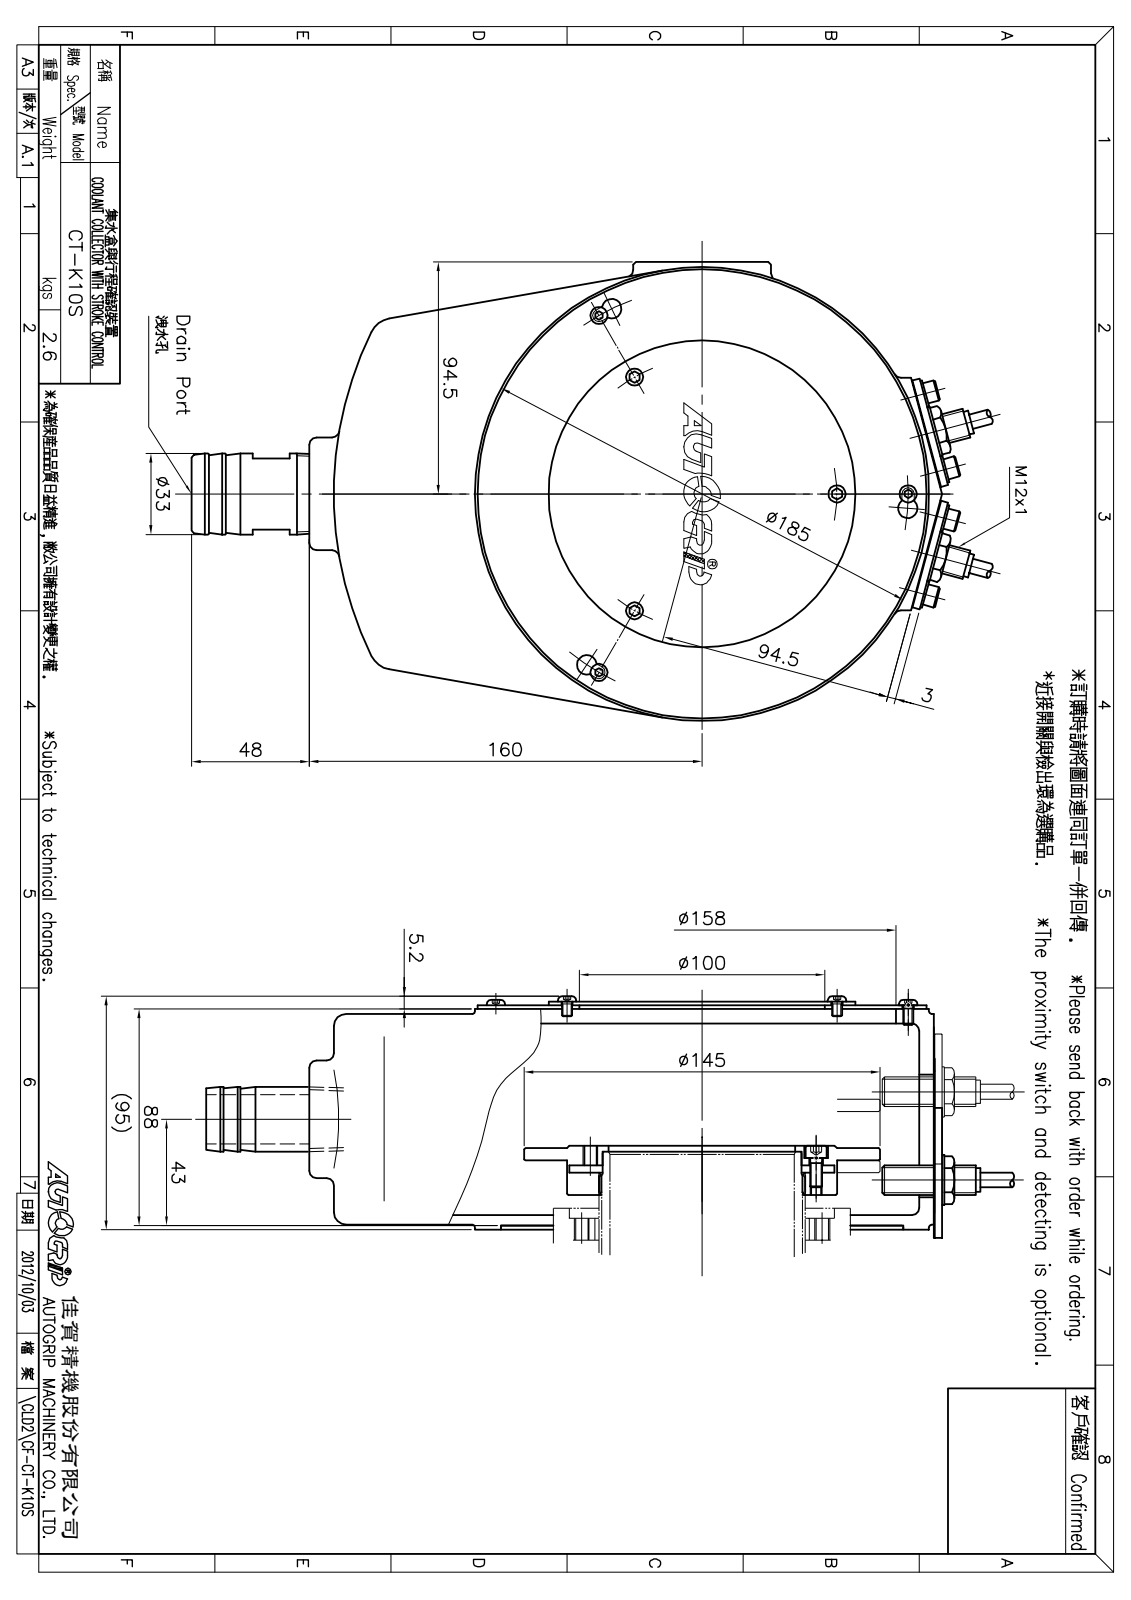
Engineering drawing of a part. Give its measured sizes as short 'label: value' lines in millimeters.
name: CF-CT-10集水盒本體; CF-CT-08洩油管; CF-CT-K10S; N5x12_M5x14 (+2 more)
written by: SolidWorks 2016 (CONFIG_CONTROL_DESIGN)
unit: mm
bodies: 25 solids, 680 faces (314 planar, 220 cylindrical, 146 other)
size: 312.28 × 187 × 95
volume: 630 546 mm³; area: 343 614 mm²
holes: 6× ⌀4, 6× ⌀5, 6× ⌀5.5, 3× ⌀4.5, 2× ⌀6, 2× ⌀9.5, 2× ⌀12, 1× ⌀25, 1× ⌀76, 1× ⌀81, 1× ⌀84, 1× ⌀100
bosses: 6× ⌀8.5, 6× ⌀7, 4× ⌀11, 2× ⌀5, 1× ⌀185, 1× ⌀183, 1× ⌀145, 1× ⌀125
rounds: 16× R2.75, 10× R2, 8× R7, 6× R1, 5× R2.5, 4× R3, 3× R4, 2× R6
face distances: 1.5, 4, 84, 6, 2, 85.5, 82, 5, 88, 73.47
hole spacings: 121.25, 22.98, 65.06, 29, 55, 84, 95.26, 27.58
